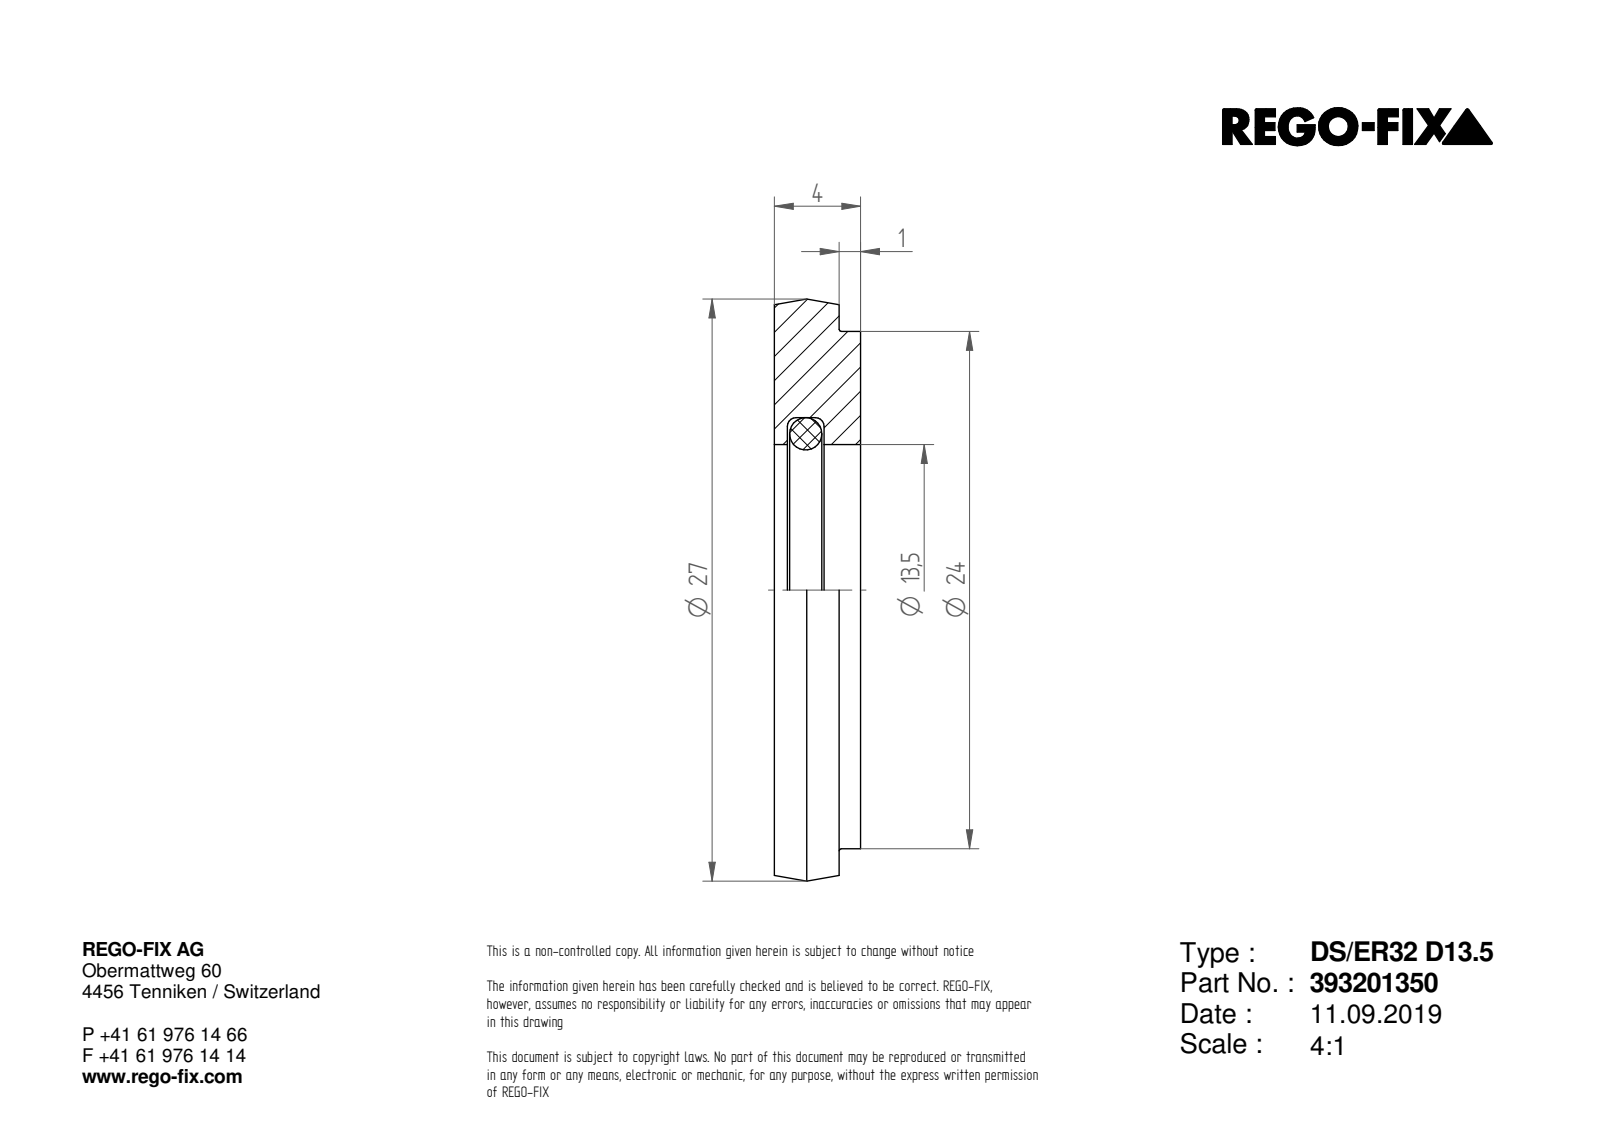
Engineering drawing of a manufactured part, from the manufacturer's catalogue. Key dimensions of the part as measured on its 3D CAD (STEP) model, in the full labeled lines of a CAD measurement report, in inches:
Part name (STEP PRODUCT): NOCUT
STEP written by: SIEMENS PLM Software Solid Edge ST10 (AUTOMOTIVE_DESIGN)
Units: inches
Bodies: 1 solid, 7 faces (3 planar, 3 cylindrical, 1 other)
Overall size (bounding box): 1.063 × 1.063 × 0.157
Volume: 0.098 in³ · Surface area: 2.1 in²
Round holes (diameter × count): ⌀0.531 ×1
Round bosses / shafts (diameter × count): ⌀1.063 ×1, ⌀0.945 ×1
Main face-to-face distances: 0.157, 0.039, 0.118
